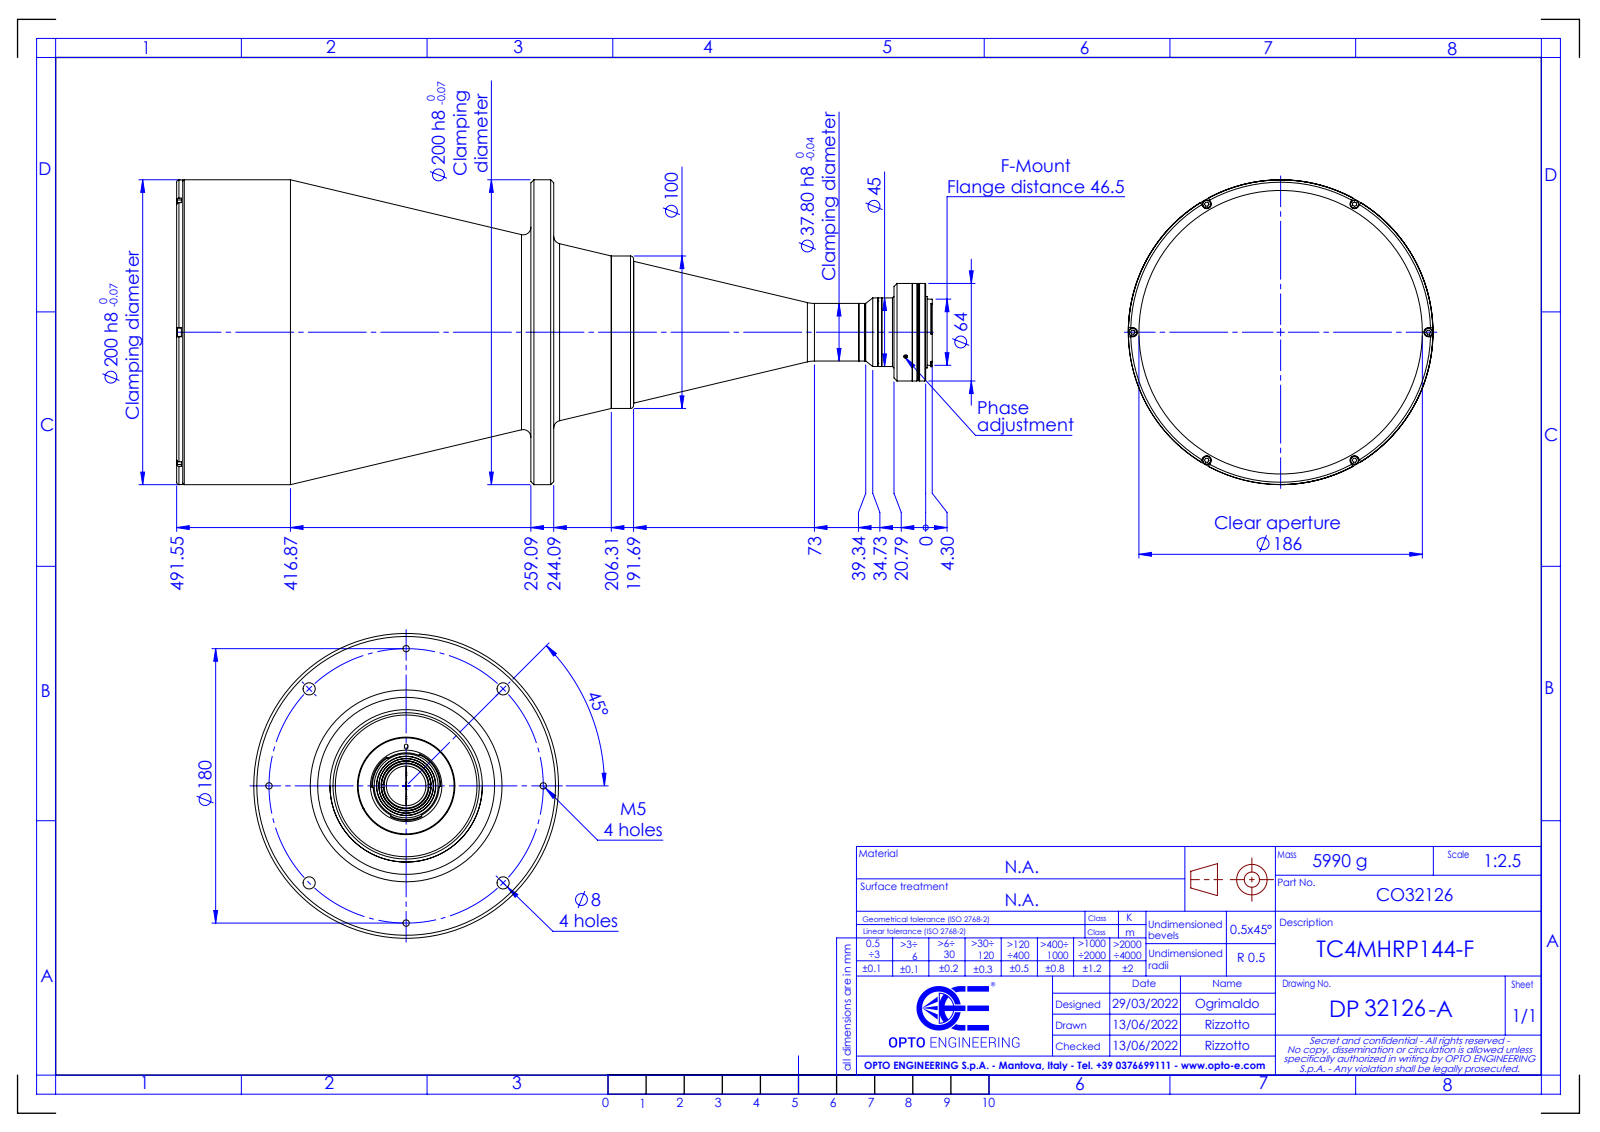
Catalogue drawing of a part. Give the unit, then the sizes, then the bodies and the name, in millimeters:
Units: millimetres
Overall size (bounding box): 495.85 × 200 × 200
Round holes (diameter × count): ⌀4.2 ×4, ⌀8 ×4, ⌀2.5 ×3, ⌀29 ×1, ⌀32 ×1, ⌀42 ×1, ⌀186 ×1, ⌀191.2 ×1
Round bosses / shafts (diameter × count): ⌀5.5 ×6, ⌀200 ×1, ⌀199.8 ×1, ⌀100 ×1, ⌀93 ×1, ⌀64 ×1, ⌀63.5 ×1, ⌀46.9 ×1
Partial cylindrical surfaces — rounded edges, fillets, slot ends (radius × count): R3 ×4, R0.5 ×2, R1.15 ×2, R22.65 ×1
Main face-to-face distances: 15, 4, 232.46, 247.46, 228.46, 243.46, 487.55, 491.55, 259.09, 244.09
Hole centre spacings: 68.88, 90, 127.28, 166.3, 180
Bodies: 0 solids, 235 faces (71 planar, 102 cylindrical, 62 other)
Part name (STEP PRODUCT): DP32126-A_TC4MHRP144-F
STEP written by: SolidWorks 2021 (CONFIG_CONTROL_DESIGN)
